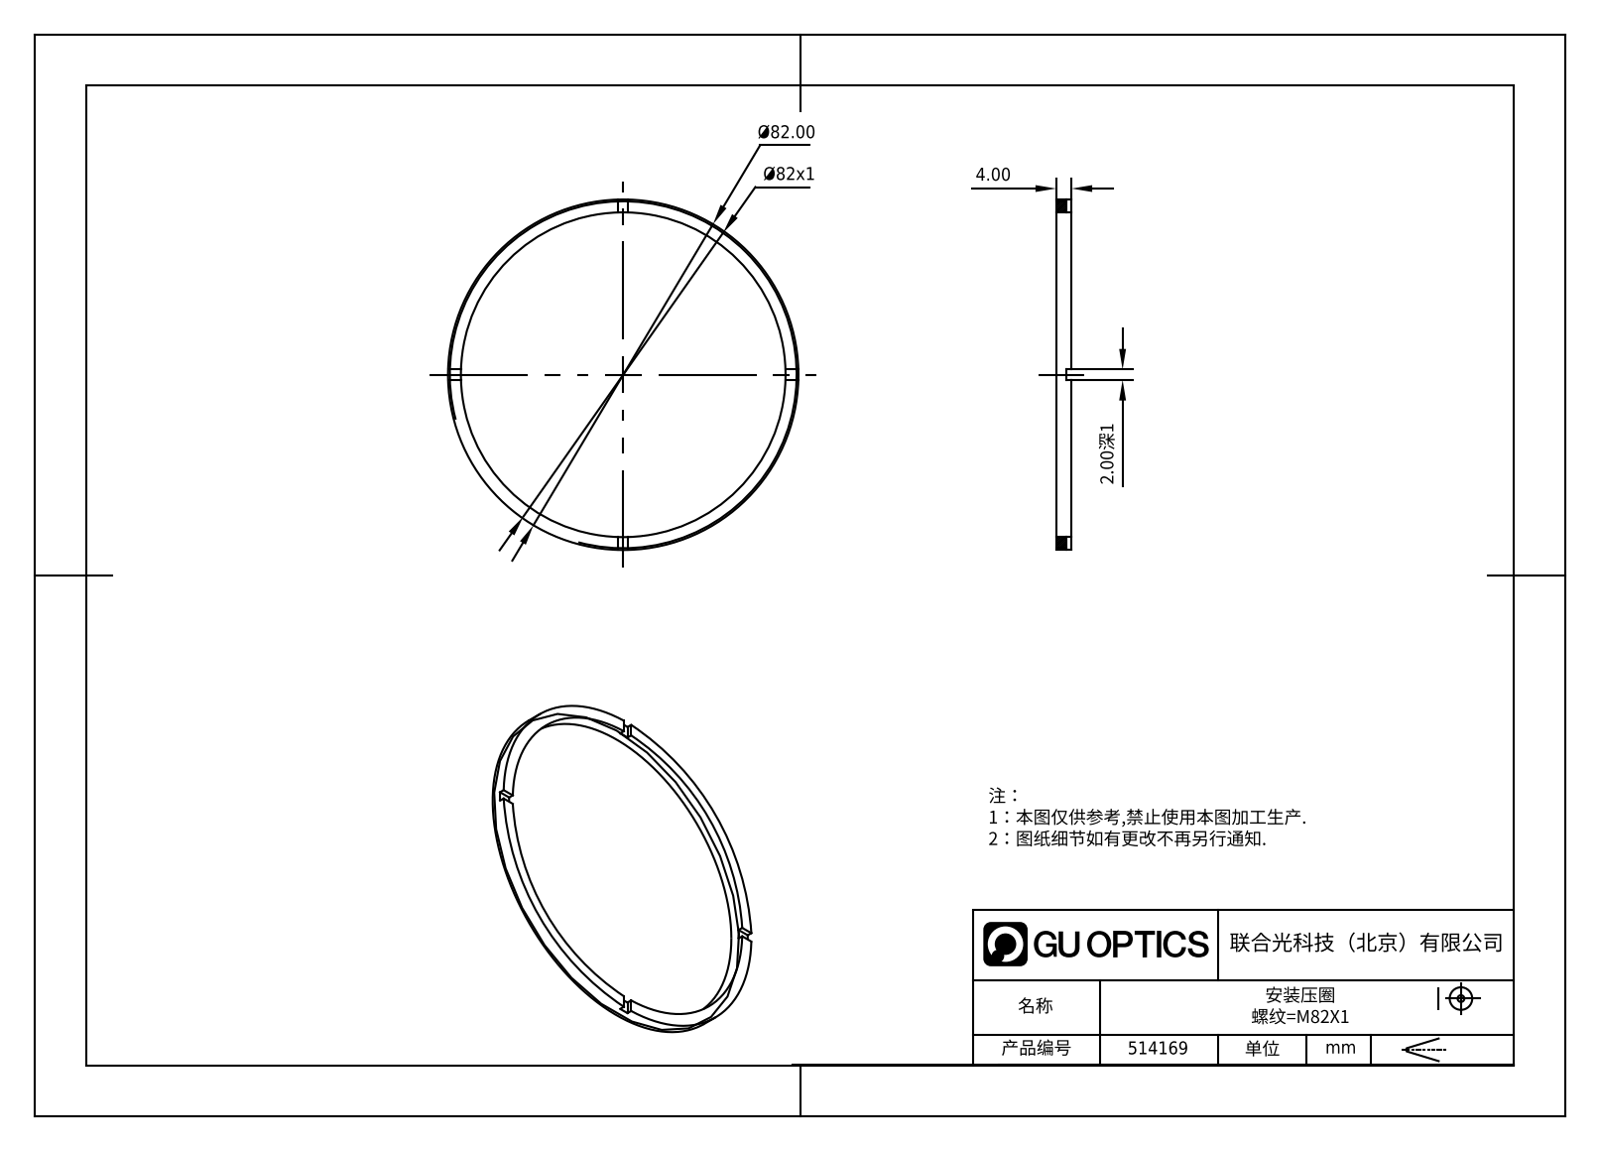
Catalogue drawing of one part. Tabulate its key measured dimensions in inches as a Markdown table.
| quantity | value |
| --- | --- |
| part name | 514169 |
| STEP written by | SolidWorks 2020 (CONFIG_CONTROL_DESIGN) |
| units | inches |
| bodies | 1 solid, 21 faces (17 planar, 4 cylindrical, 0 other) |
| overall size | 3.228 × 3.228 × 0.157 |
| volume | 0.18 in³ |
| surface area | 5.399 in² |
| round holes (diameter × count) | 2.992 × 1 |
| round bosses / shafts (diameter × count) | 3.228 × 1 |
| main face-to-face distances | 0.157, 0.118, 0.039, 0.079 |
